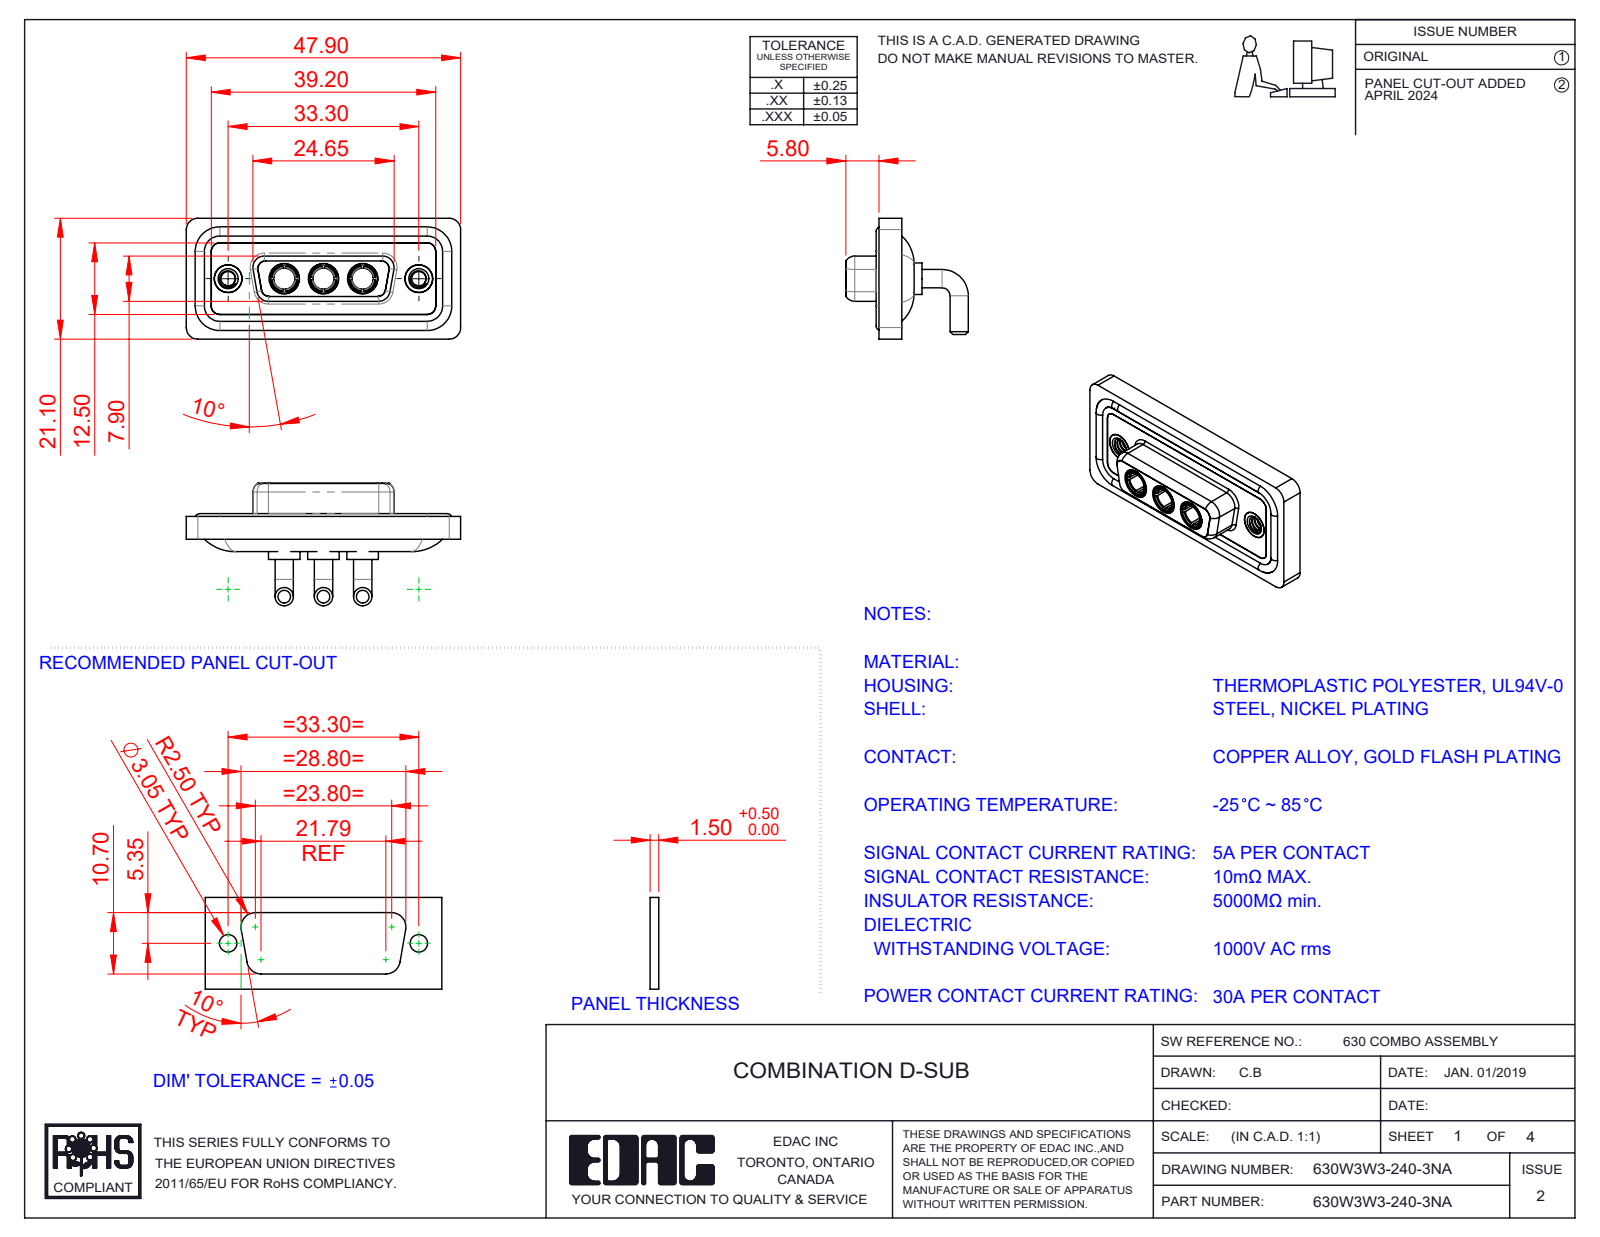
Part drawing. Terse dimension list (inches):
name: 630Combo Shell Front_15 Contacts; 630Combo Housing_3W3; Power Socket_30A RA; 630Combo Shell Rear_15 Contacts (+3 more)
written by: SolidWorks 2023 (CONFIG_CONTROL_DESIGN)
unit: in
bodies: 13 solids, 614 faces (192 planar, 261 cylindrical, 161 other)
size: 1.886 × 0.843 × 0.831
volume: 0.382 in³; area: 15.55 in²
holes: 5× ⌀0.191, 3× ⌀0.146, 3× ⌀0.209, 2× ⌀0.098, 2× ⌀0.157, 2× ⌀0.159, 2× ⌀0.197
bosses: 6× ⌀0.126, 4× ⌀0.063, 3× ⌀0.217, 3× ⌀0.205, 3× ⌀0.195, 3× ⌀0.187, 3× ⌀0.148, 2× ⌀0.195
rounds: 20× R0.079, 18× R0.059, 12× R0.053, 8× R0.063, 4× R0.01, 4× R0.02, 4× R0.024, 4× R0.026
face distances: 0.016, 0.071, 0.043, 0.063, 0.114, 0.098, 0.122, 0.146, 0.161, 0.059
hole spacings: 0.27, 0.386, 0.656, 0.925, 0.539, 1.311
